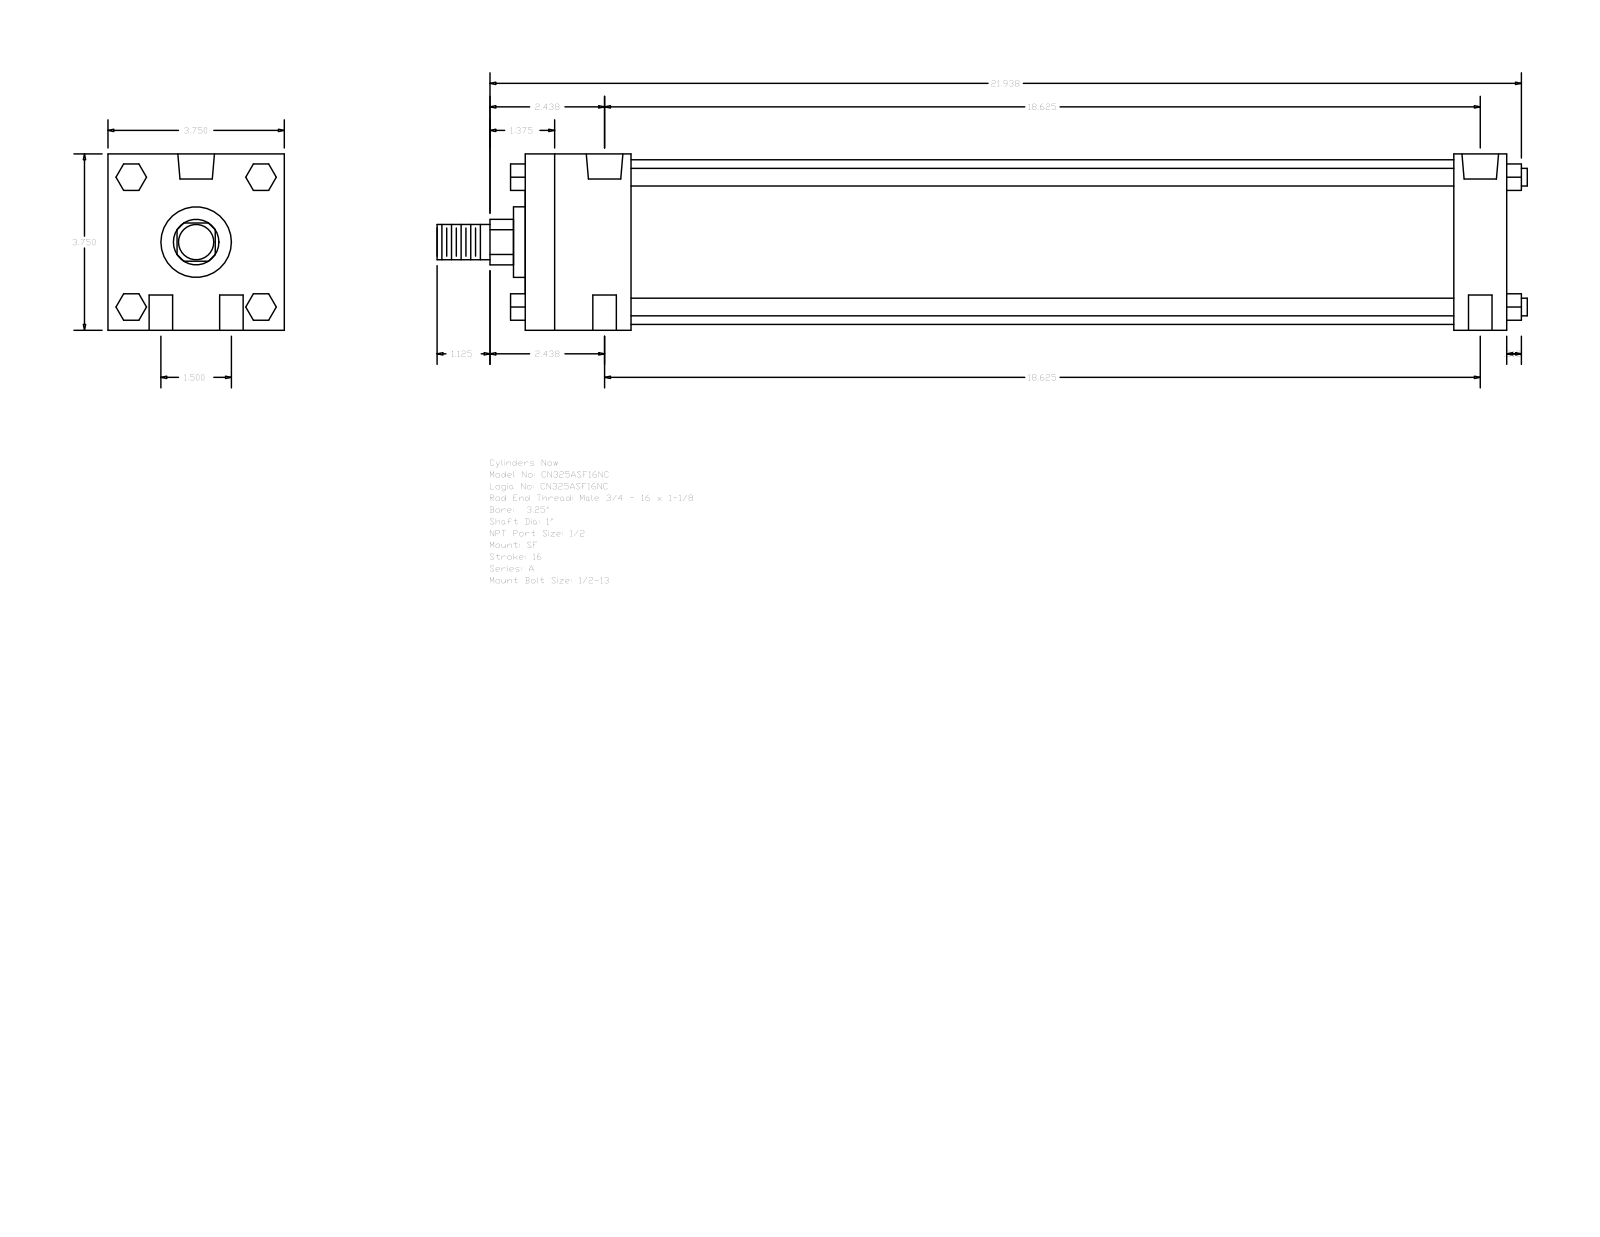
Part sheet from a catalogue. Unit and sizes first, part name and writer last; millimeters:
Units: millimetres
Overall size (bounding box): 588.96 × 95.25 × 95.25
Round holes (diameter × count): ⌀12.7 ×4, ⌀8.73 ×2, ⌀19.77 ×2
Round bosses / shafts (diameter × count): ⌀9.53 ×4, ⌀88.9 ×1, ⌀38.1 ×1, ⌀25.4 ×1, ⌀19.05 ×1
Partial cylindrical surfaces — rounded edges, fillets, slot ends (radius × count): R12.29 ×1
Main face-to-face distances: 95.24, 530.22, 28.57, 501.65, 57.15, 444.5, 473.07, 14.28, 35.05, 60.71
Hole centre spacings: 19.05, 473.46, 473.08, 38.1, 474.61, 466.72
Bodies: 0 solids, 124 faces (94 planar, 30 cylindrical, 0 other)
Part name (STEP PRODUCT): A_SF__0325_1
STEP written by: GSSL Pune (CONFIG_CONTROL_DESIGN)
